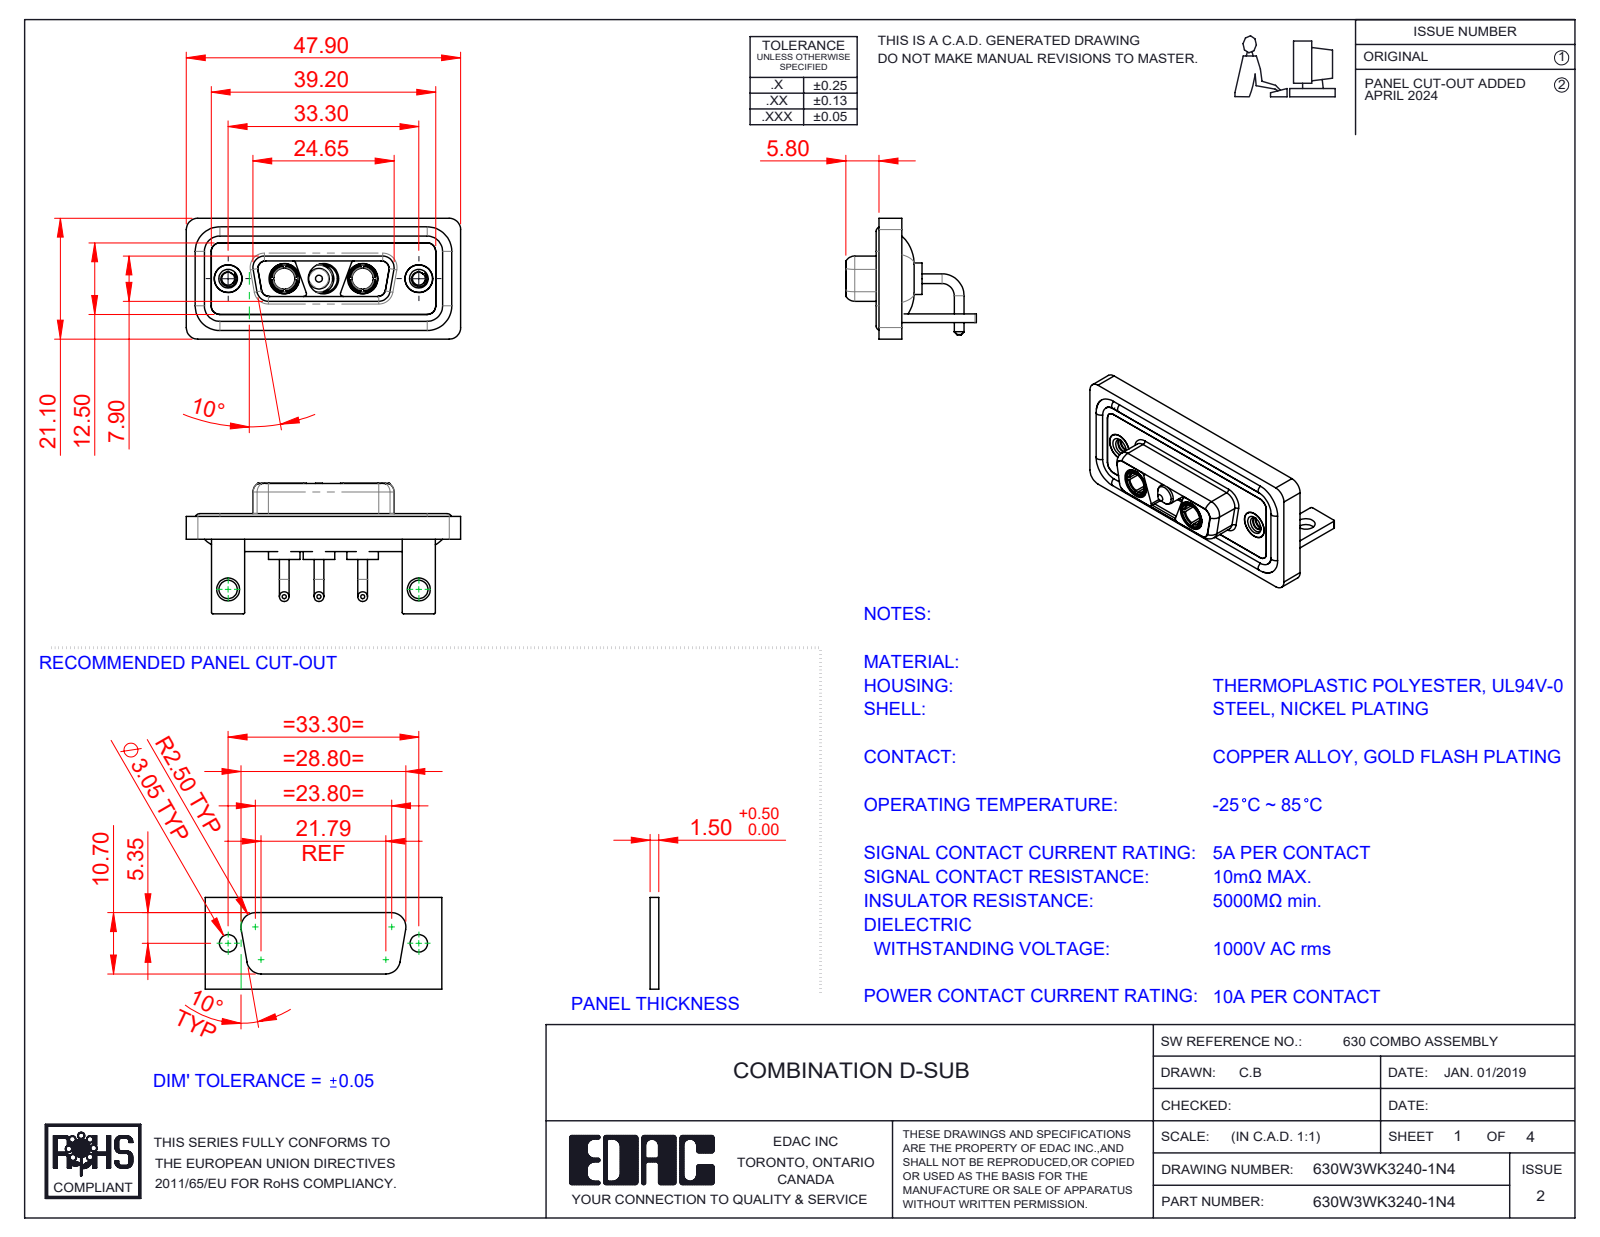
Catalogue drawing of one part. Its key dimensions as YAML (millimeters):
part_name: "630Combo Shell Front_15 Contacts; 630Combo Waterproof Housing_15 Contacts; 630Combo Housing_3WK3; Power Pin_10A RA (+5 more)"
step_written_by: "SolidWorks 2023 (CONFIG_CONTROL_DESIGN)"
units: millimeters
bodies: {solids: 15, faces: 643, planar: 198, cylindrical: 288, other: 157}
overall_size: [47.9, 22.8, 21.1]
volume: 6225
surface_area: 10321
round_holes:
  - {diameter: 4.85, count: 5}
  - {diameter: 5.3, count: 3}
  - {diameter: 2.26, count: 2}
  - {diameter: 3.2, count: 2}
  - {diameter: 3.7, count: 2}
  - {diameter: 4, count: 2}
  - {diameter: 4.05, count: 2}
  - {diameter: 5, count: 2}
round_bosses_or_shafts:
  - {diameter: 1.7, count: 6}
  - {diameter: 1.6, count: 4}
  - {diameter: 5.5, count: 3}
  - {diameter: 5.2, count: 3}
  - {diameter: 4.75, count: 3}
  - {diameter: 3.75, count: 3}
  - {diameter: 4.96, count: 2}
  - {diameter: 4.95, count: 2}
partial_cylinders:
  - {radius: 2, count: 21}
  - {radius: 1.5, count: 18}
  - {radius: 0.25, count: 16}
  - {radius: 1.35, count: 12}
  - {radius: 0.5, count: 9}
  - {radius: 1.6, count: 8}
  - {radius: 0.6, count: 4}
  - {radius: 0.65, count: 4}
face_to_face_distances: [0.4, 2.9, 1.5, 3.7, 1.8, 1.1, 4.1, 1.6, 2.5, 1.4]
hole_center_spacings: [6.85, 9.8, 16.65, 23.5, 33.3, 13.7]
